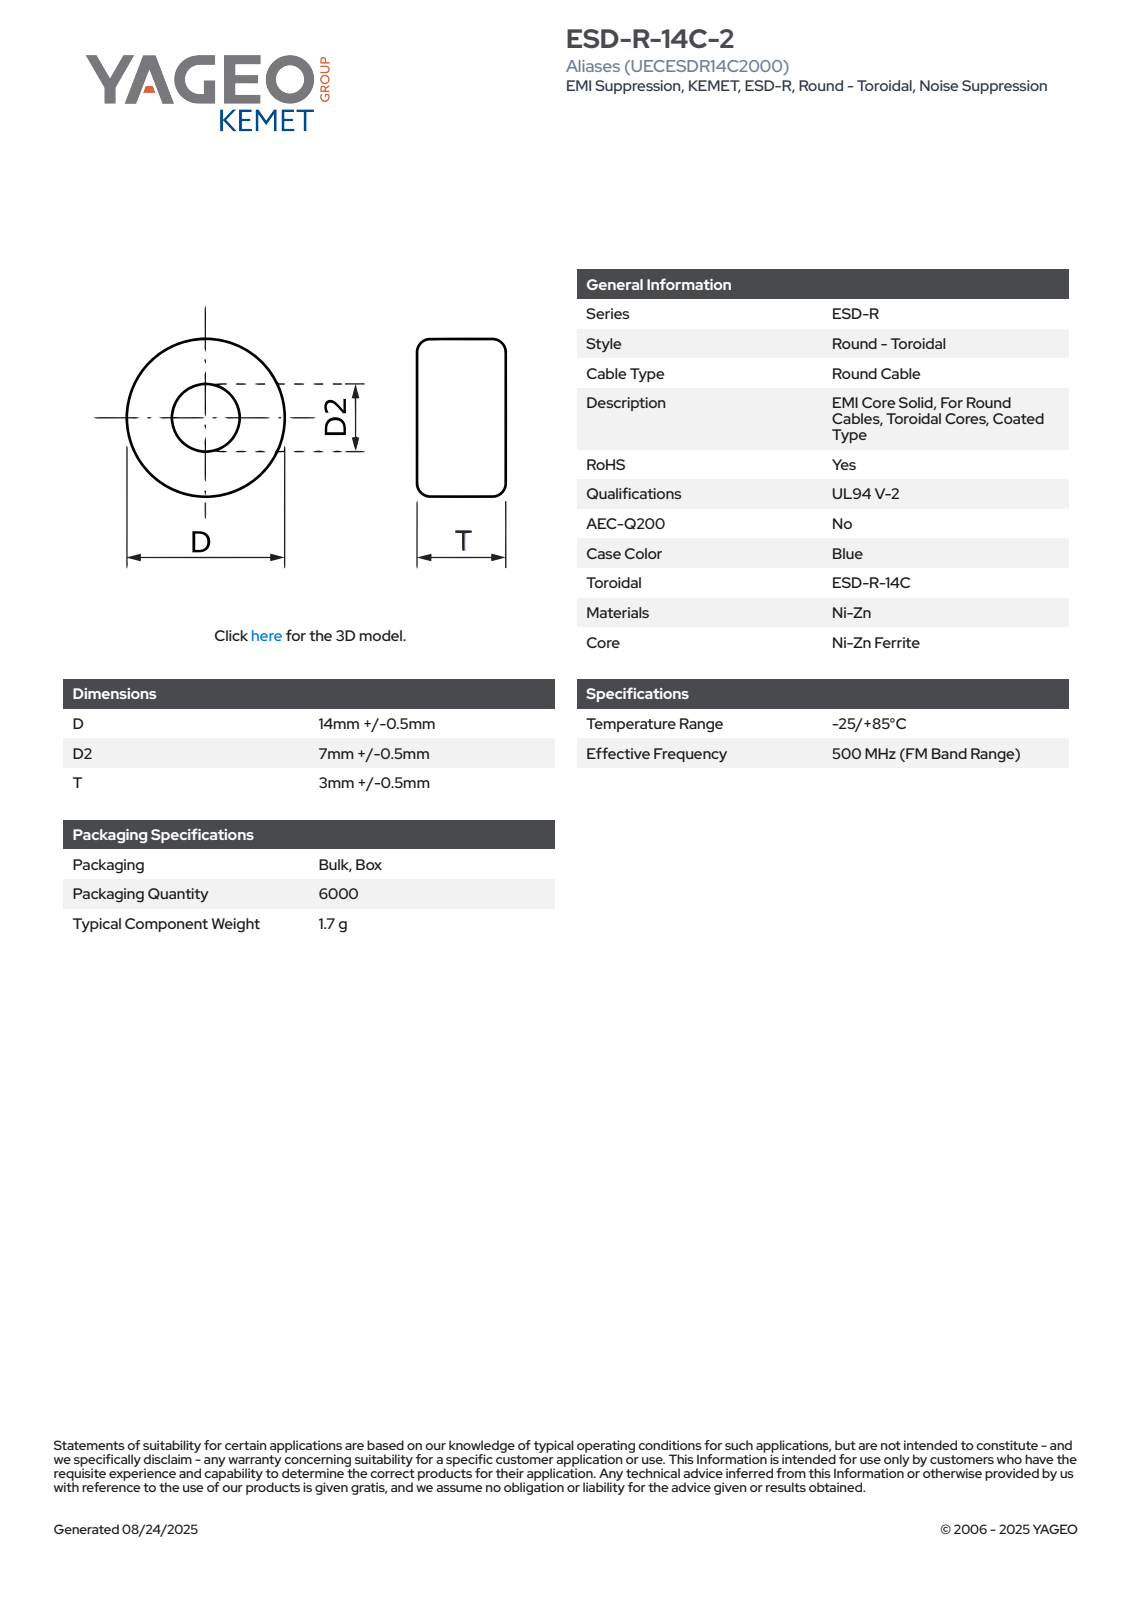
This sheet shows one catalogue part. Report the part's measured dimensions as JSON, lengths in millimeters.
{"part_name": "EC_KBC_D14.5D27T3.5", "step_written_by": "SolidWorks 2021 (AUTOMOTIVE_DESIGN)", "units": "millimeters", "bodies": {"solids": 1, "faces": 66, "planar": 24, "cylindrical": 7, "other": 35}, "overall_size": [14.51, 14.5, 3.5], "volume_mm3": 439, "surface_area_mm2": 474, "round_holes": [[7, 1]], "round_bosses_or_shafts": [[14.5, 1]], "partial_cylinders_radius": [[7.26, 1]], "face_to_face_distances": [3.5, 0.9, 2.6, 1.7, 0.32, 1.22, 2.28, 1.38, 1.06, 1.96]}
